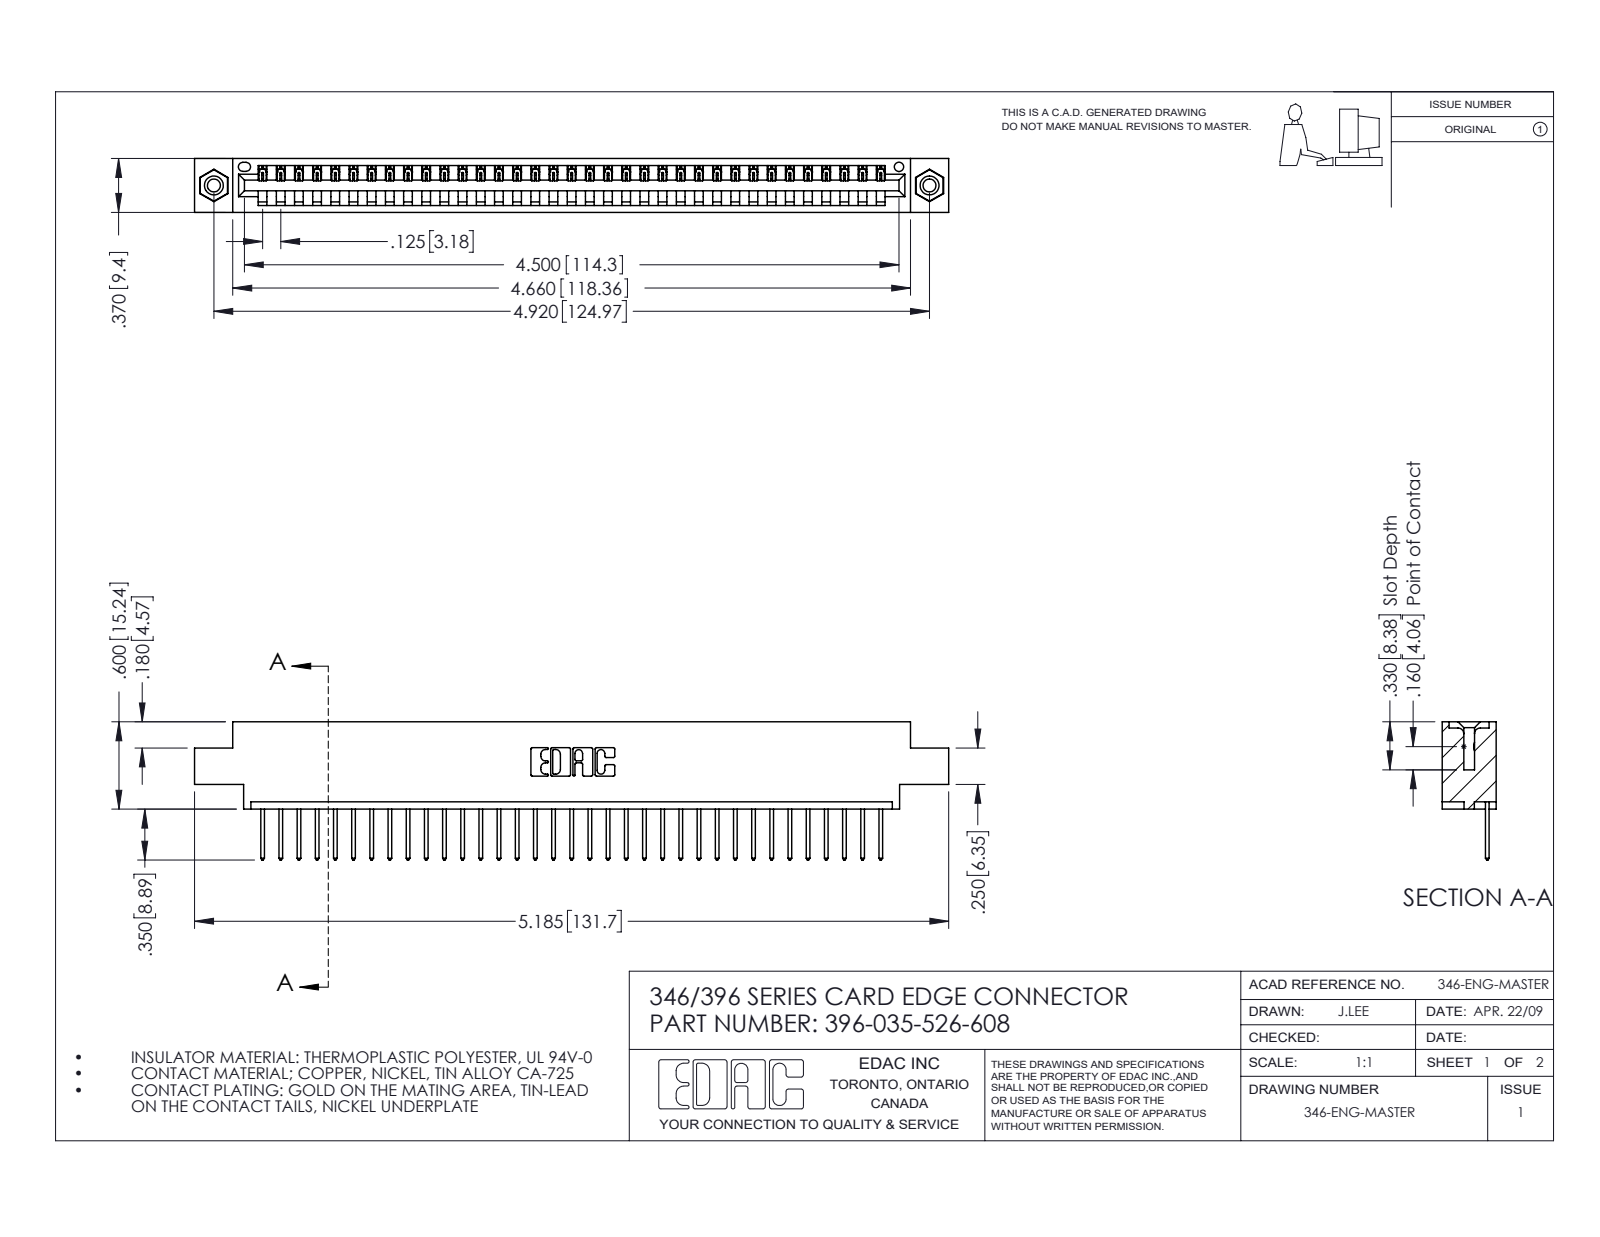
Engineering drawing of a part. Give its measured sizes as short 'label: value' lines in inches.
name: 396-035-526-608; 345-250-001_345-250-003-102; 345-292-001_345-293-126; 346 Part_0.170 Offset - 0.156 Dia-TI
written by: SolidWorks 2016 (CONFIG_CONTROL_DESIGN)
unit: in
bodies: 38 solids, 2216 faces (1512 planar, 688 cylindrical, 16 other)
size: 5.185 × 0.95 × 0.37
volume: 0.755 in³; area: 24.08 in²
holes: 2× ⌀0.089, 2× ⌀0.125, 2× ⌀0.156, 1× ⌀0.064
bosses: 2× ⌀0.155
rounds: 70× R0.006, 70× R0.01, 22× R0.01, 6× R0.007, 6× R0.031, 3× R0.026, 2× R0.031, 2× R0.04
face distances: 0.048, 0.322, 0.37, 0.25, 0.072, 0.298, 0.025, 0.222, 0.148, 0.1
hole spacings: 0.246, 4.711, 4.92
